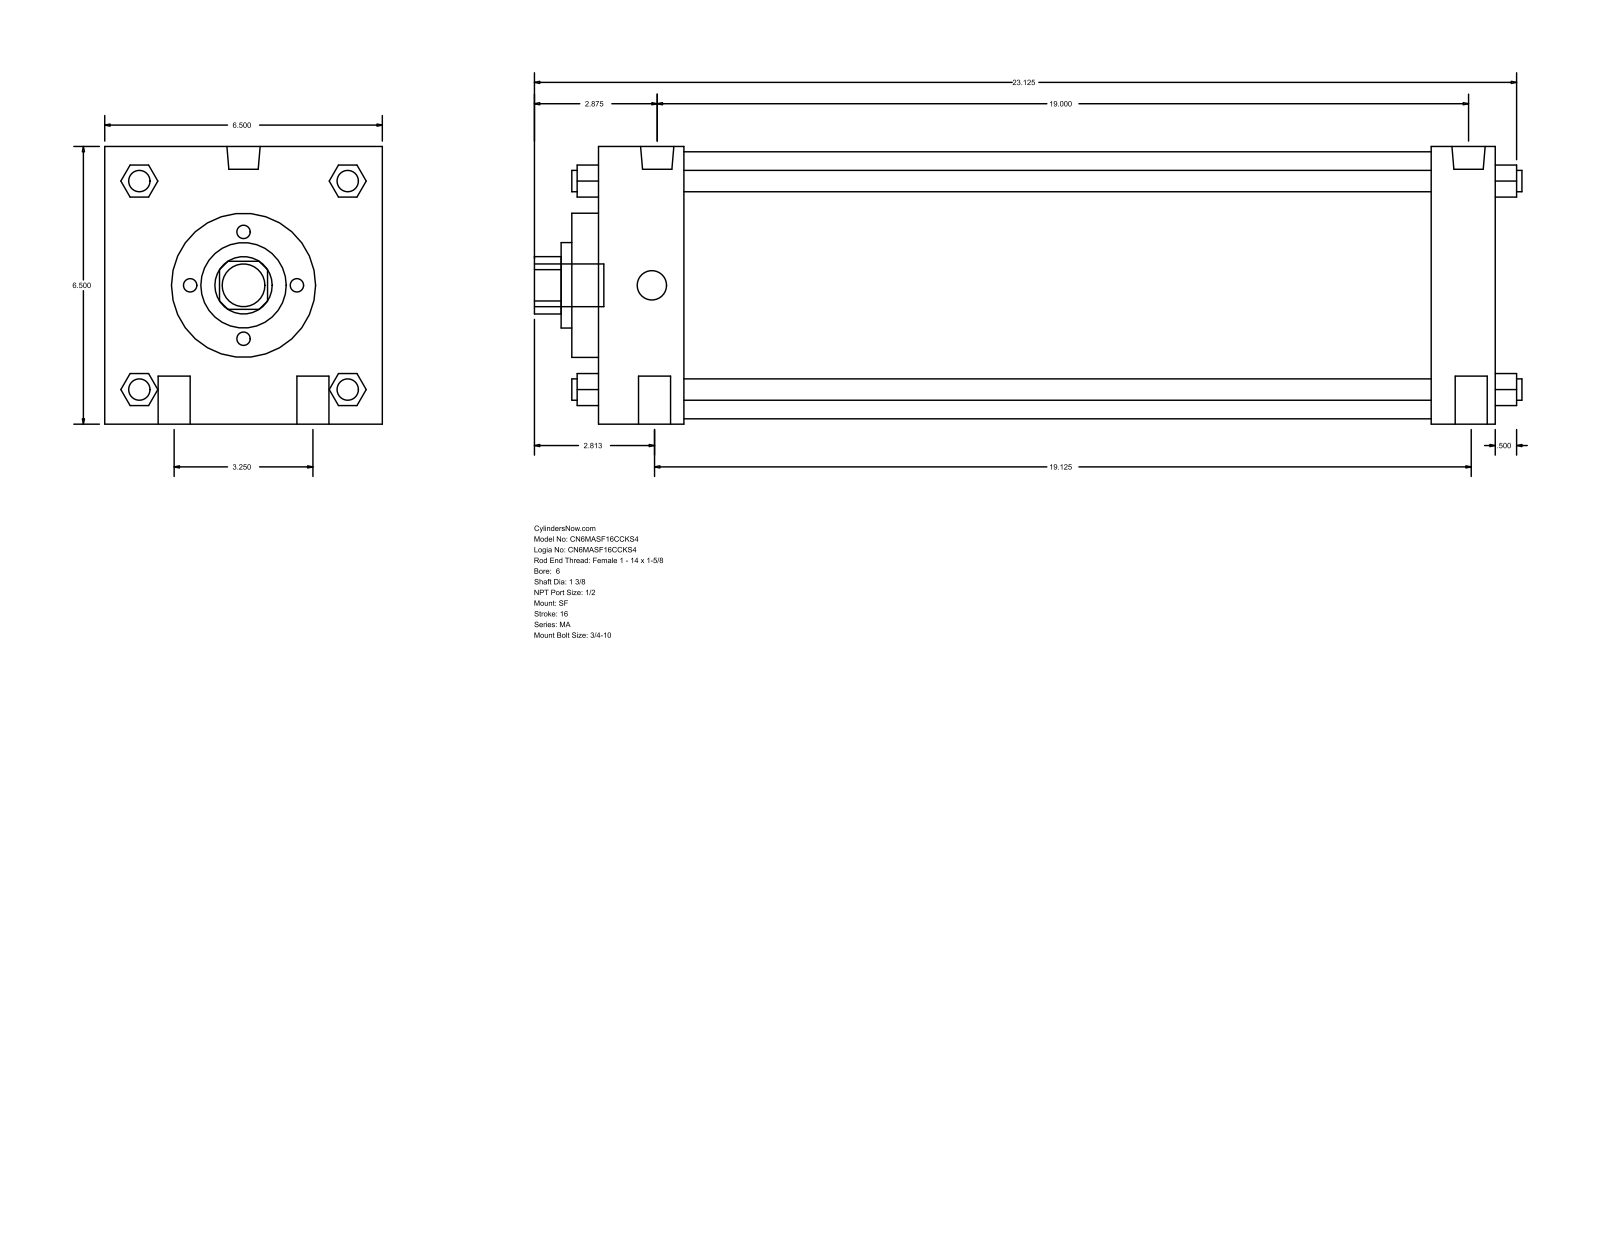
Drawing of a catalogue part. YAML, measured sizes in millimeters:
part_name: "MA_SF__0600_1.375"
step_written_by: "GSSL Pune (CONFIG_CONTROL_DESIGN)"
units: millimeters
bodies: {solids: 0, faces: 126, planar: 95, cylindrical: 31, other: 0}
overall_size: [587.38, 165.1, 165.1]
round_holes:
  - {diameter: 34.92, count: 1}
  - {diameter: 50.8, count: 1}
  - {diameter: 85.72, count: 1}
  - {diameter: 158.75, count: 1}
round_bosses_or_shafts:
  - {diameter: 19.05, count: 4}
  - {diameter: 12.7, count: 4}
  - {diameter: 19.77, count: 2}
  - {diameter: 17.46, count: 2}
  - {diameter: 25.4, count: 1}
partial_cylinders:
  - {radius: 17.06, count: 1}
face_to_face_distances: [165.1, 533.4, 495.3, 50.8, 38.1, 444.5, 482.6, 15.87, 66.67, 511.17]
